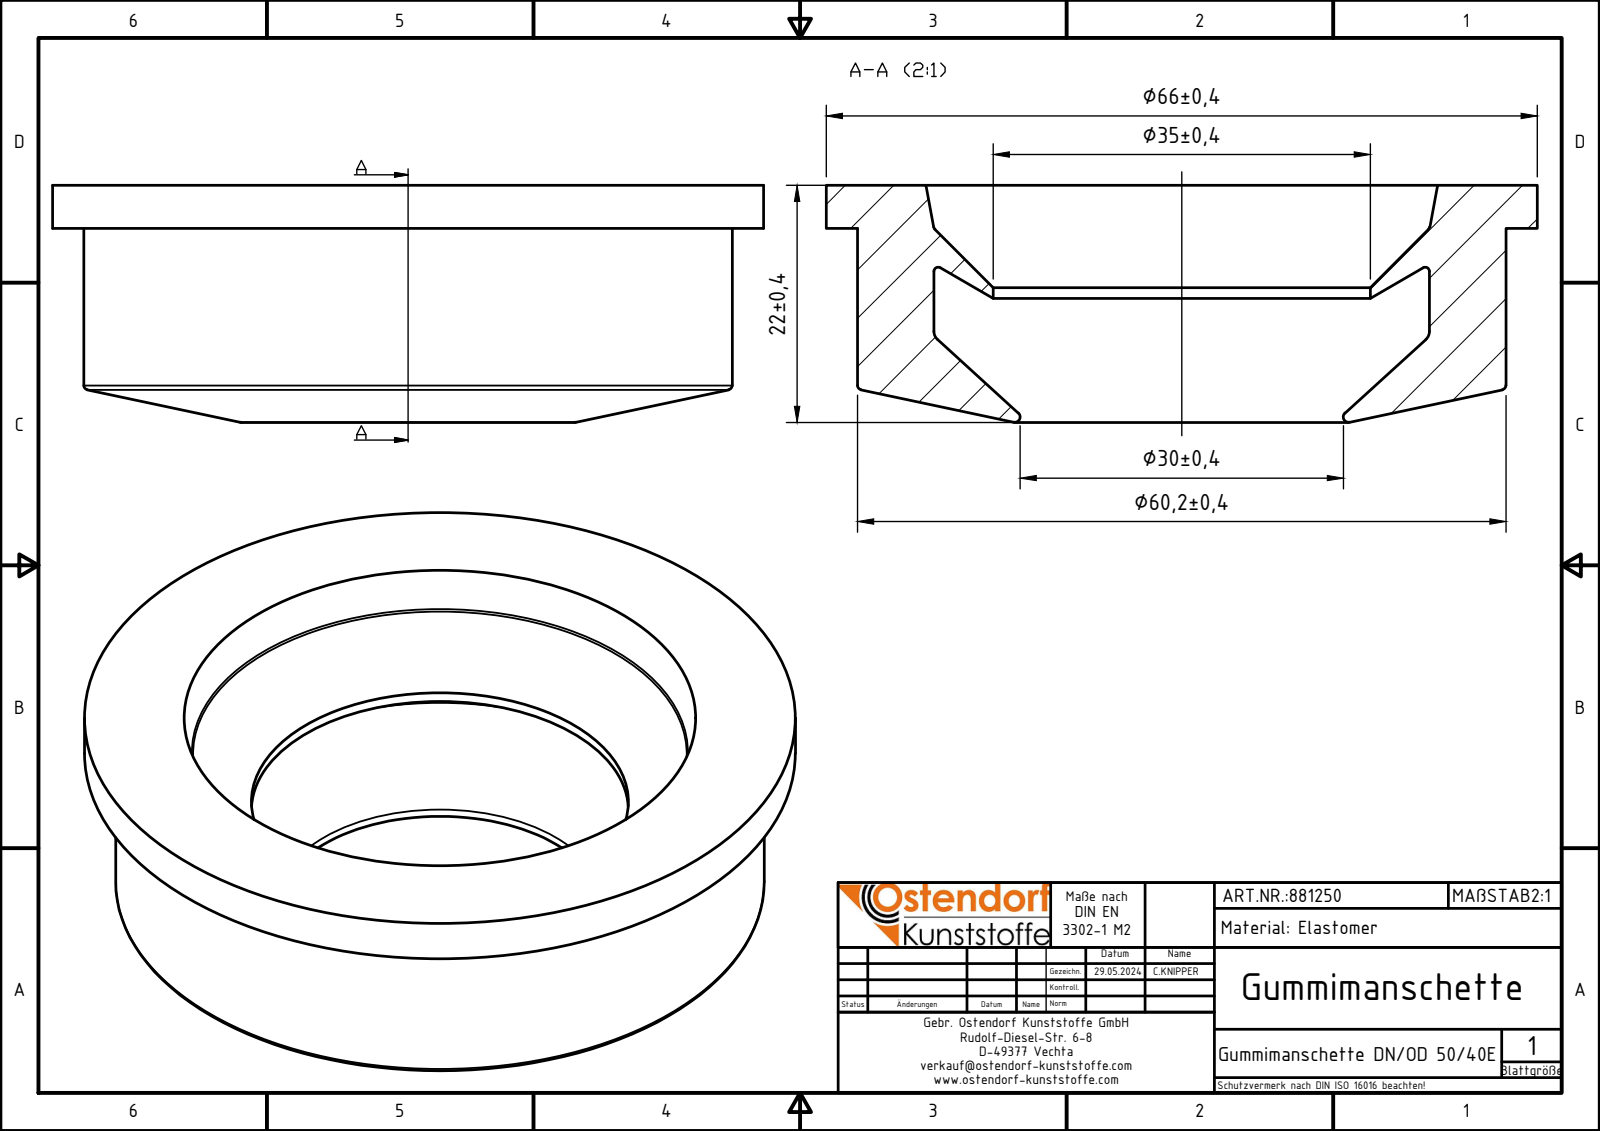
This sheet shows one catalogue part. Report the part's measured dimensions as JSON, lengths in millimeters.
{"part_name": "881250z", "step_written_by": "Autodesk Inventor 2024 (AUTOMOTIVE_DESIGN)", "units": "millimeters", "bodies": {"solids": 1, "faces": 16, "planar": 2, "cylindrical": 4, "other": 10}, "overall_size": [66, 66, 22], "volume_mm3": 30530, "surface_area_mm2": 12762, "round_holes": [[35, 1], [46, 1]], "round_bosses_or_shafts": [[66, 1], [60.2, 1]], "face_to_face_distances": [4]}
